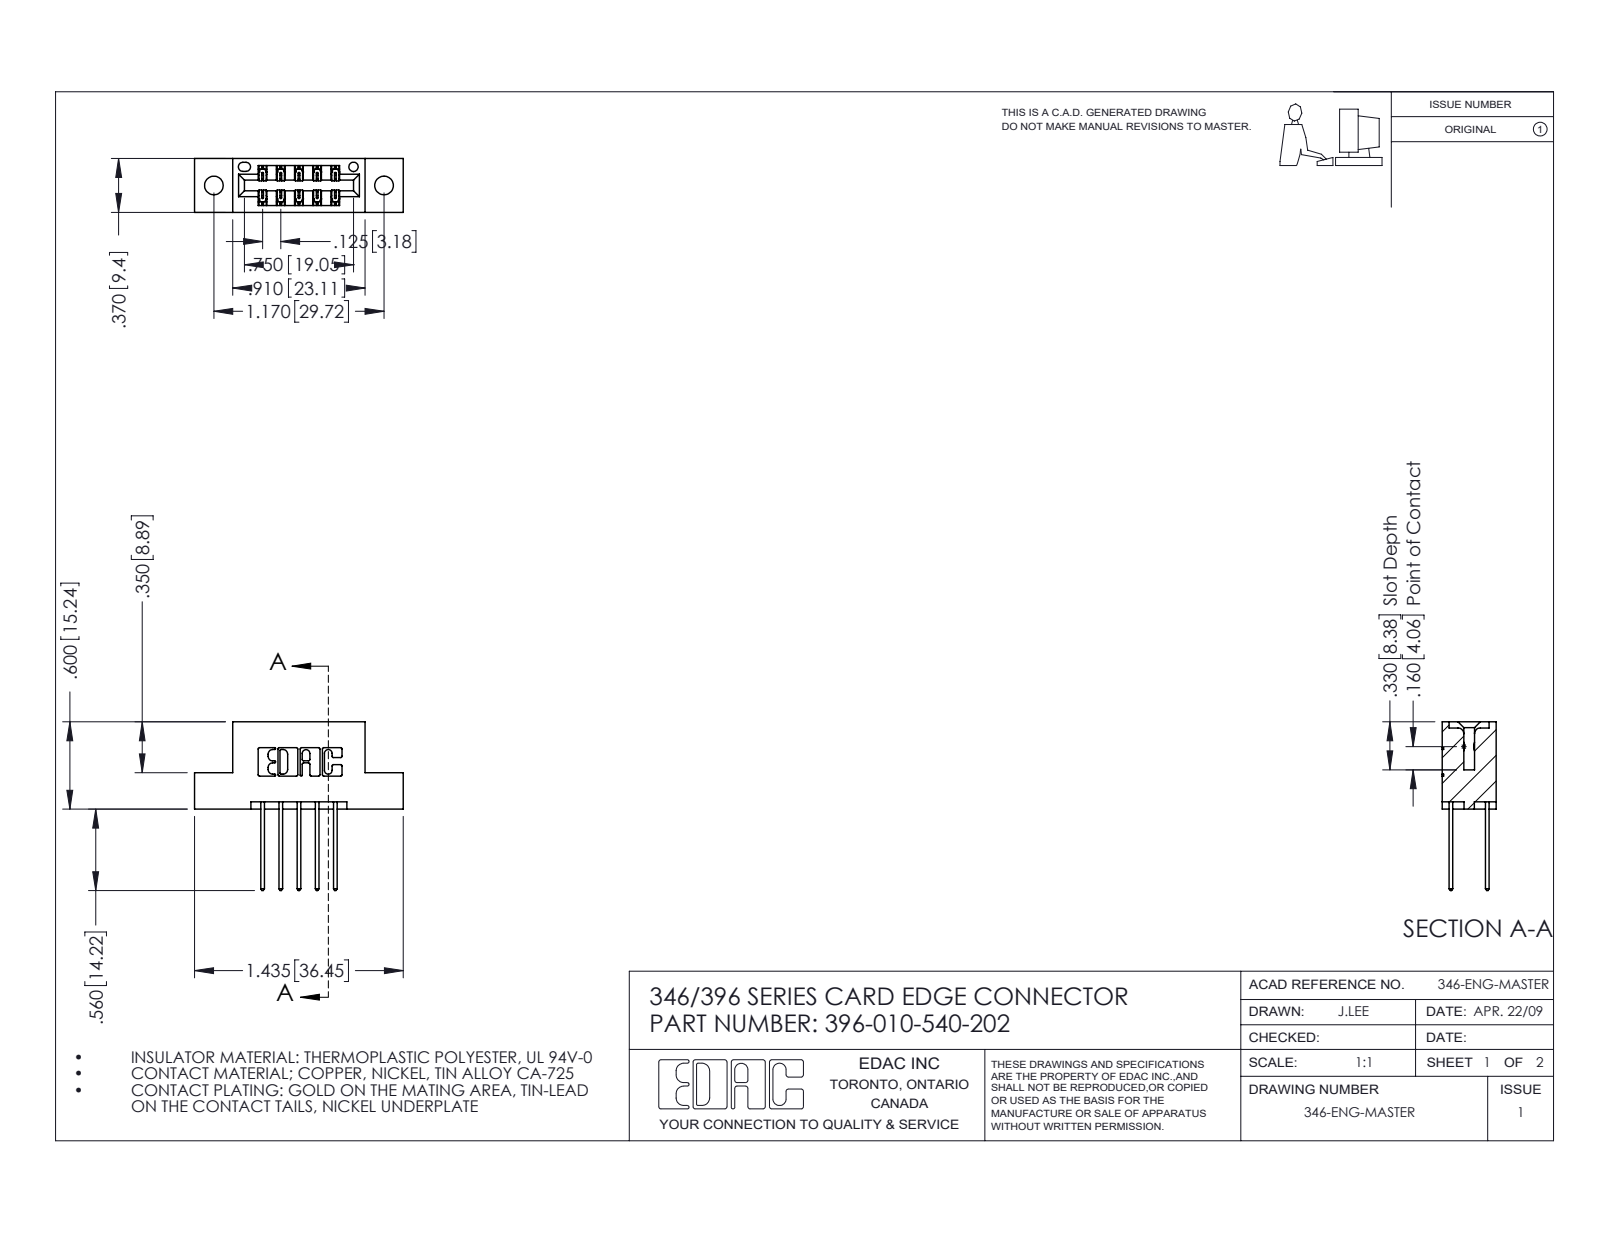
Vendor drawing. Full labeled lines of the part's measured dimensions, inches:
Part name (STEP PRODUCT): 345-292-001_345-293-140; 346 Part_Flush Mounting Lugs - 0.128 Dia; 396-010-540-202
STEP written by: SolidWorks 2016 (CONFIG_CONTROL_DESIGN)
Units: inches
Bodies: 11 solids, 642 faces (426 planar, 216 cylindrical, 0 other)
Overall size (bounding box): 1.435 × 1.16 × 0.37
Volume: 0.199 in³ · Surface area: 5.922 in²
Round holes (diameter × count): ⌀0.128 ×2, ⌀0.064 ×1
Partial cylindrical surfaces — rounded edges, fillets, slot ends (radius × count): R0.01 ×22, R0.006 ×15, R0.01 ×10, R0.007 ×6, R0.031 ×6, R0.026 ×3, R0.014 ×2, R0.022 ×2
Main face-to-face distances: 0.25, 0.048, 0.322, 0.37, 0.025, 0.072, 0.298, 0.275, 0.125, 0.125
Hole centre spacings: 0.246, 0.969, 1.17
